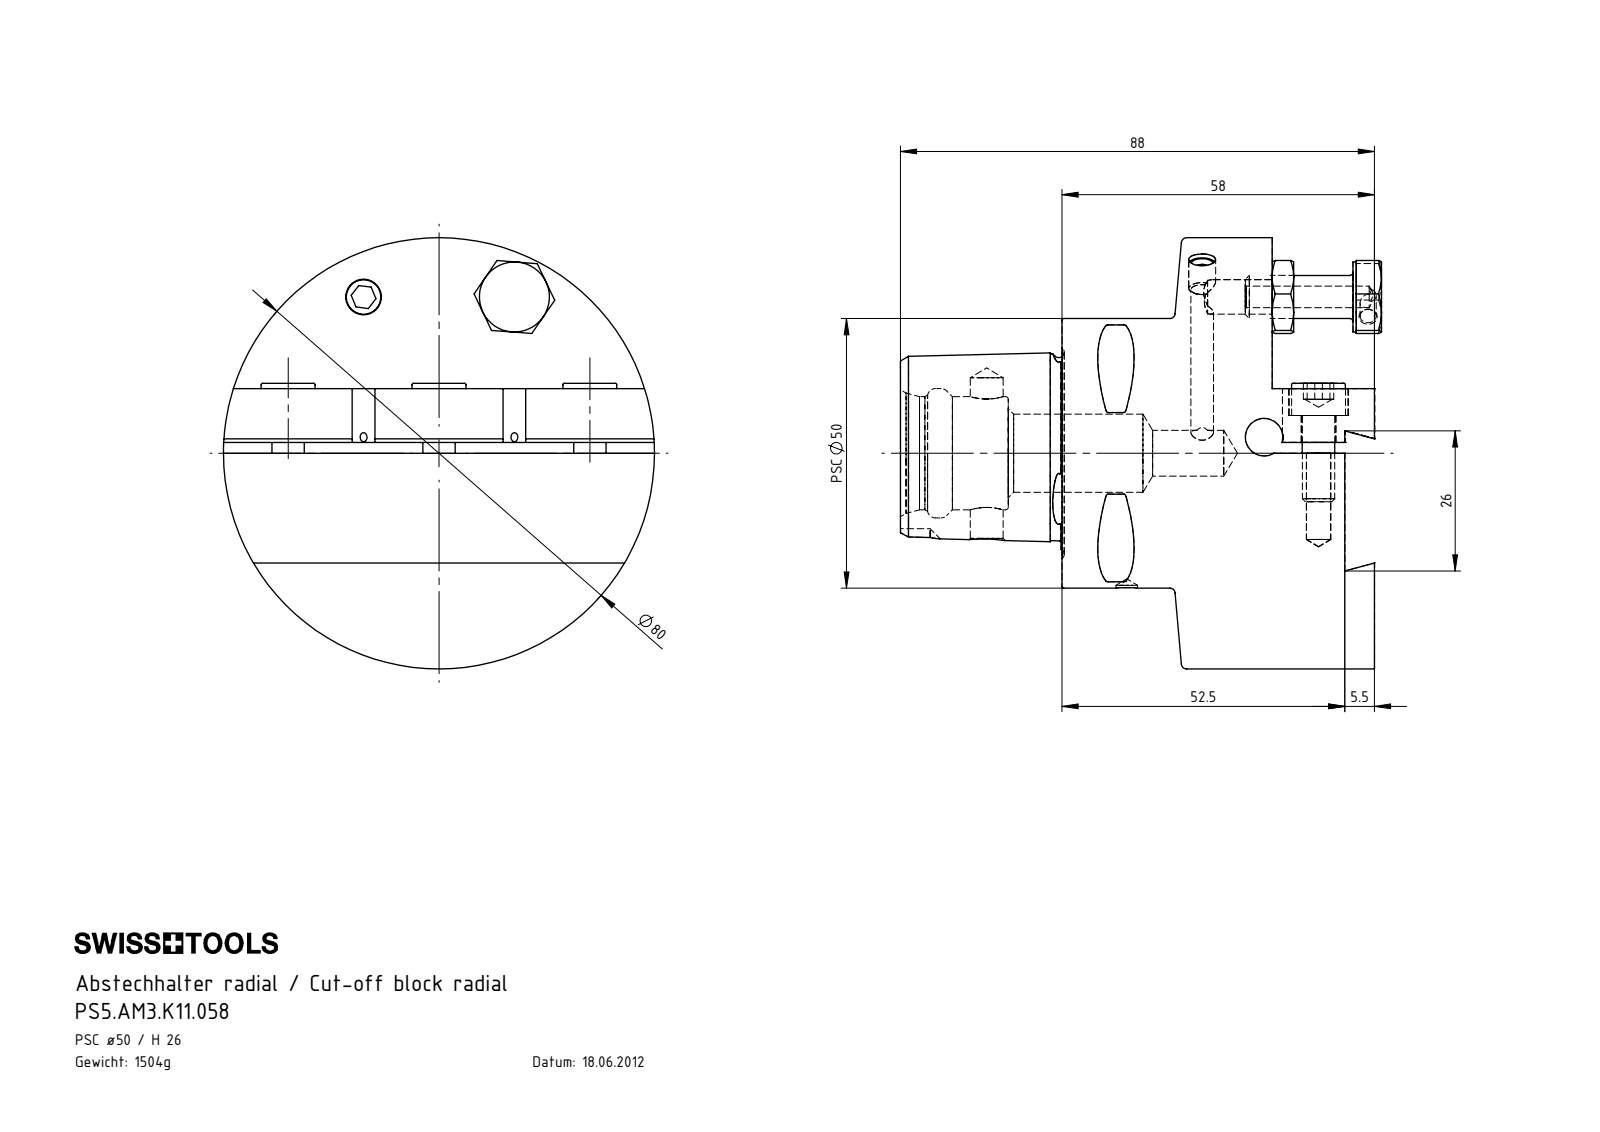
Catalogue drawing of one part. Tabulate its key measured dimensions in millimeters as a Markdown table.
| quantity | value |
| --- | --- |
| part name | ISO 4035 - M8_PreviewCfg; ISO 4762 - M6 x 16_PreviewCfg; PS5-AM3.K11.058_A; ISO 4026 - M8 x 10_PreviewCfg (+3 more) |
| STEP written by | SolidWorks 2017 (AUTOMOTIVE_DESIGN) |
| units | millimeters |
| bodies | 11 solids, 436 faces (124 planar, 106 cylindrical, 206 other) |
| overall size | 89.3 × 80 × 80 |
| volume | 193 919 mm³ |
| surface area | 39 648 mm² |
| round holes (diameter × count) | 6.4 × 5, 4 × 4, 5 × 3, 11 × 3, 4.2 × 2, 7 × 2, 3 × 1, 6.1 × 1, 8.5 × 1, 14.5 × 1, 21 × 1, 24 × 1 |
| round bosses / shafts (diameter × count) | 10 × 3, 6 × 3, 8 × 2, 5 × 2, 80 × 1, 50 × 1, 13 × 1 |
| partial cylindrical surfaces (radius × count) | 0.5 × 8, 2.1 × 2, 4 × 1 |
| main face-to-face distances | 14.5, 19, 4.5, 12, 2.4, 9.6, 39, 53.5, 58, 4 |
| hole center spacings | 28, 32.2, 45.21, 67.57, 26, 35.5, 56, 61.5 |
